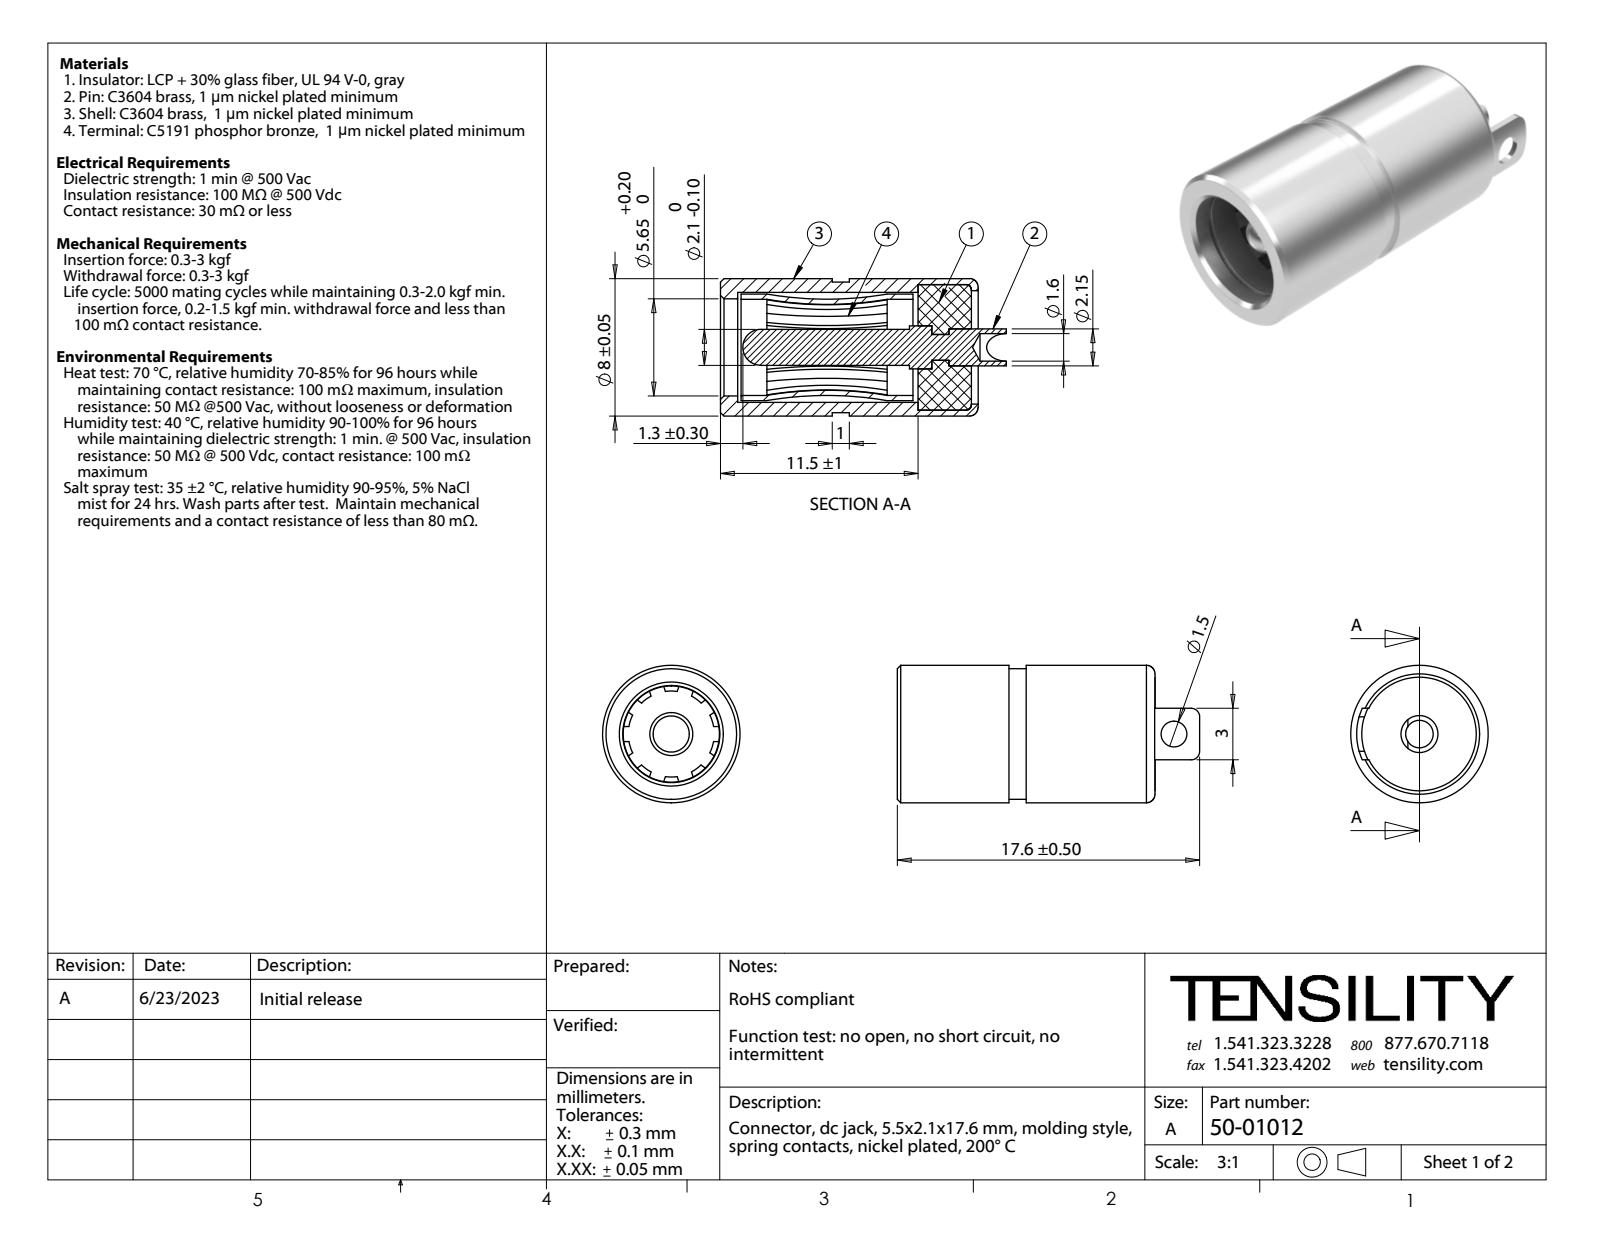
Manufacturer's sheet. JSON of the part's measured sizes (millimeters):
{"part_name": "50-01012_revA; 50-01012 insulator_Insulator; 50-01012 center pin_Center pin; 50-01012 shell_Shell (+1 more)", "step_written_by": "SolidWorks 2021 (CONFIG_CONTROL_DESIGN)", "units": "millimeters", "bodies": {"solids": 4, "faces": 160, "planar": 68, "cylindrical": 50, "other": 42}, "overall_size": [17.6, 8, 8], "volume_mm3": 445, "surface_area_mm2": 1366, "round_holes": [[1.5, 2], [1.6, 1], [2.15, 1], [2.5, 1], [5.6, 1], [5.65, 1], [6.4, 1], [6.6, 1]], "round_bosses_or_shafts": [[8, 1], [7.6, 1], [7.3, 1], [6.2, 1], [2.1, 1]], "partial_cylinders_radius": [[0.5, 2], [3.35, 1]], "face_to_face_distances": [3.1, 14.6, 11.5, 1, 0.87, 12.3, 5.3, 6.5, 5.8, 8.5]}
